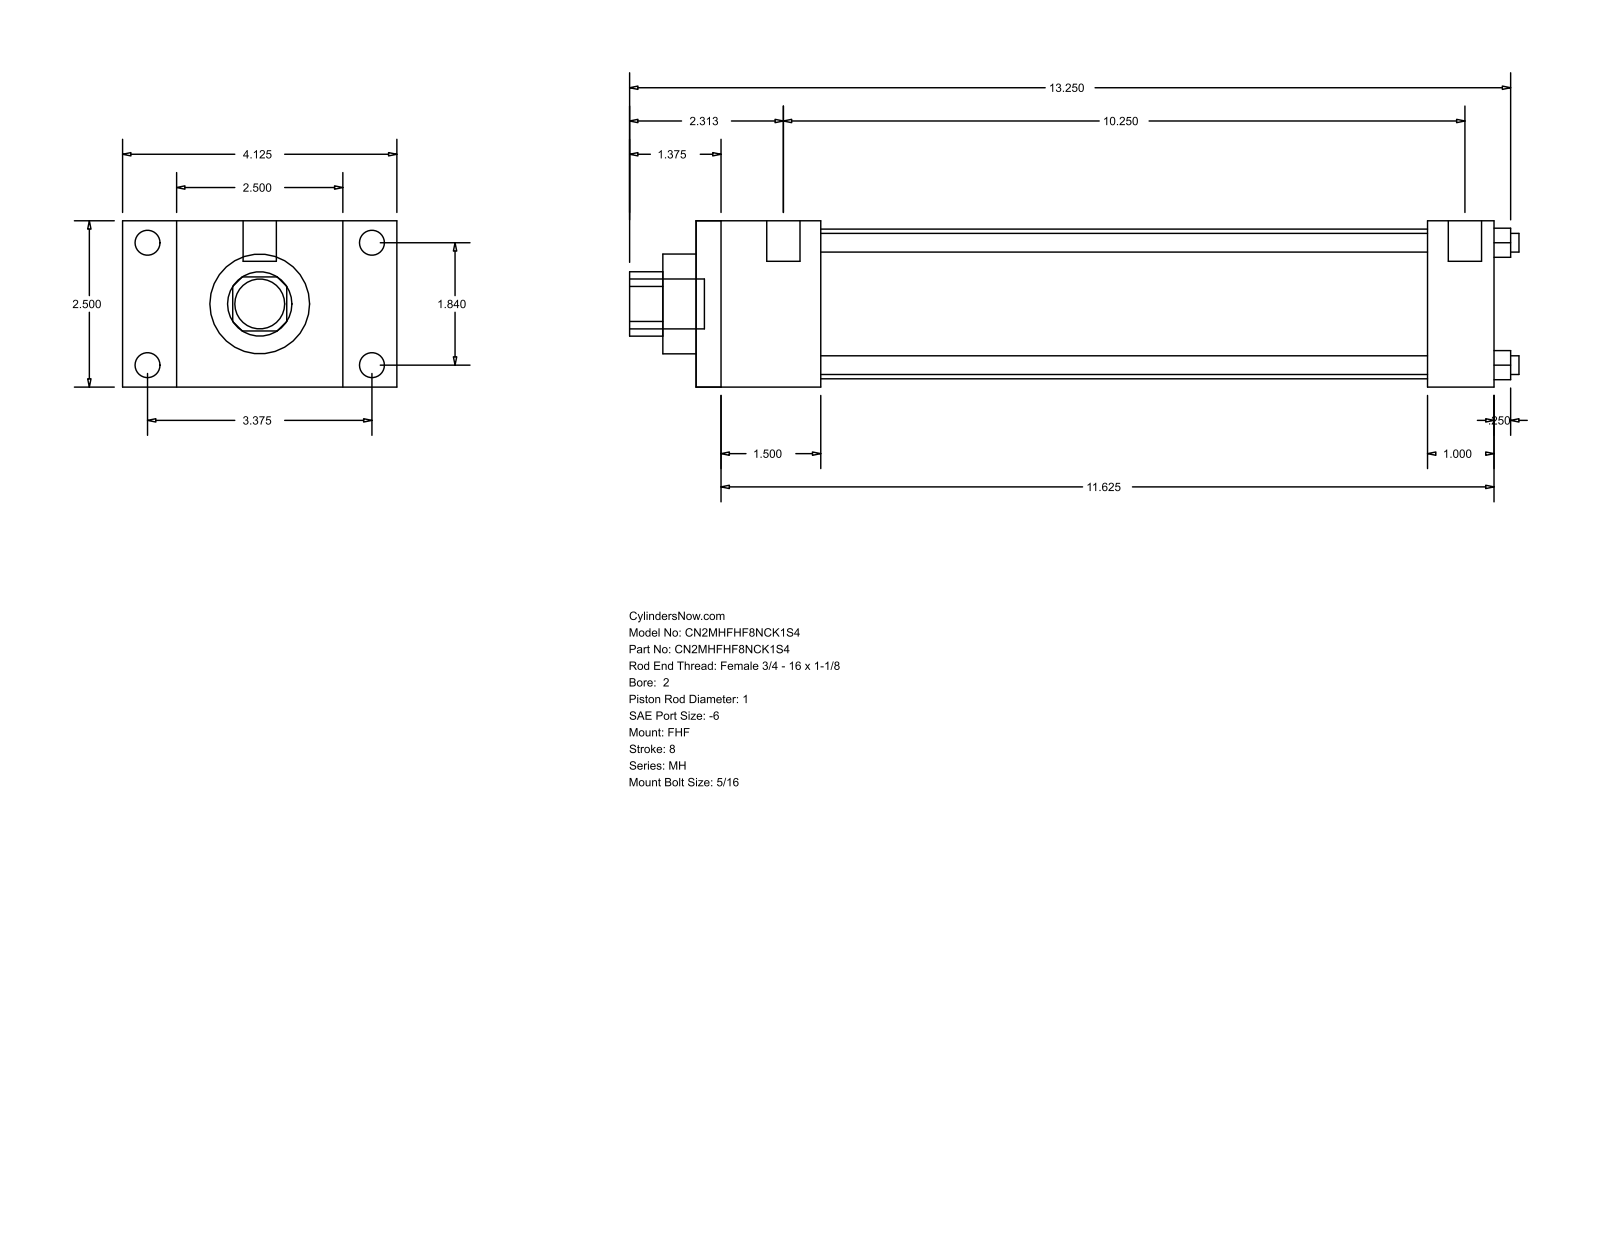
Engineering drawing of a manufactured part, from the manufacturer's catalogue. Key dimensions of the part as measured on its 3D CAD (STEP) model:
Part name (STEP PRODUCT): MH_FHF__0200_1
STEP written by: GSSL Pune (CONFIG_CONTROL_DESIGN)
Units: millimetres
Bodies: 0 solids, 88 faces (60 planar, 28 cylindrical, 0 other)
Overall size (bounding box): 339.73 × 104.78 × 63.5
Round holes (diameter × count): ⌀7.14 ×4, ⌀25.4 ×1, ⌀38.1 ×1, ⌀57.15 ×1
Round bosses / shafts (diameter × count): ⌀9.53 ×4, ⌀5.56 ×4, ⌀12.7 ×2, ⌀19.05 ×1
Partial cylindrical surfaces — rounded edges, fillets, slot ends (radius × count): R12.29 ×1
Main face-to-face distances: 63.5, 304.8, 47.63, 257.17, 20.64, 84.14, 104.78, 25.4, 279.4, 231.77
Hole centre spacings: 33.05, 46.74, 66.1
